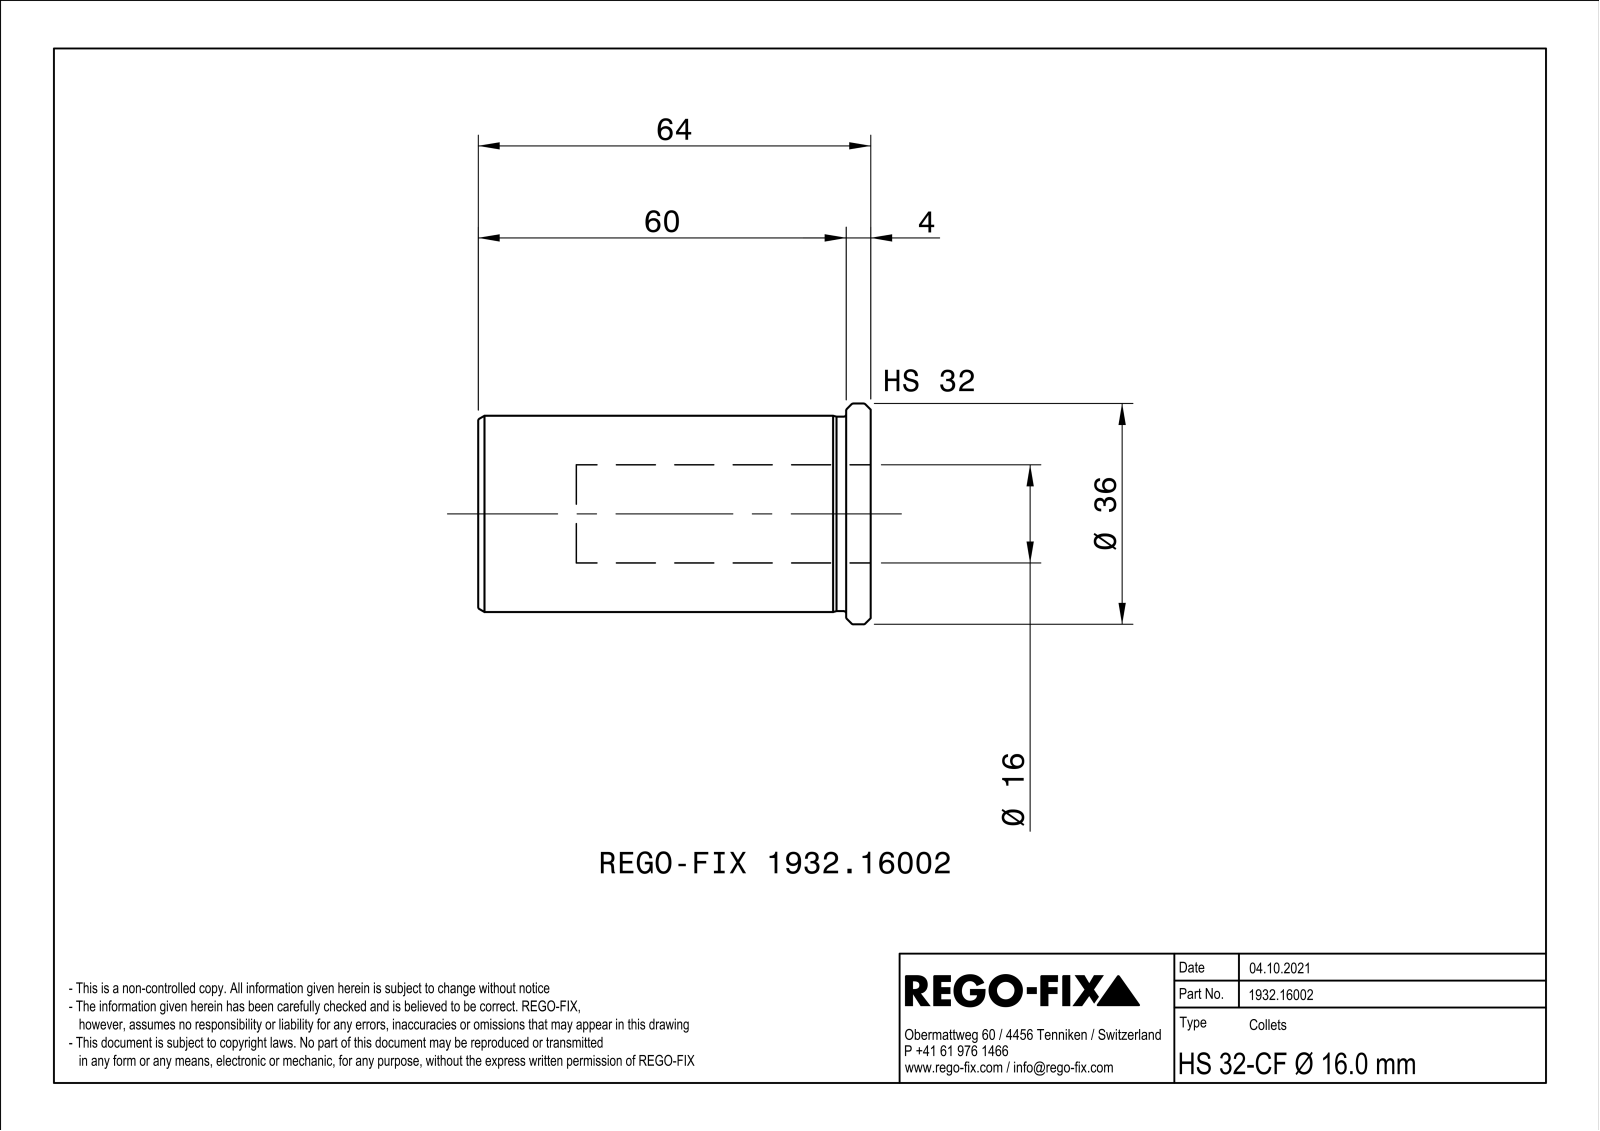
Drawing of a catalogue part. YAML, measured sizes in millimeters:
part_name: "NOCUT"
step_written_by: "SIEMENS PLM Software Solid Edge ST10 (AUTOMOTIVE_DESIGN)"
units: millimeters
bodies: {solids: 1, faces: 80, planar: 14, cylindrical: 26, other: 40}
overall_size: [64, 35.99, 35.99]
volume: 32810
surface_area: 14360
round_holes:
  - {diameter: 16, count: 1}
  - {diameter: 26.5, count: 1}
round_bosses_or_shafts:
  - {diameter: 36, count: 1}
  - {diameter: 32, count: 1}
  - {diameter: 31.7, count: 1}
partial_cylinders:
  - {radius: 0.5, count: 6}
  - {radius: 0.75, count: 4}
face_to_face_distances: [1, 64, 4, 60]
